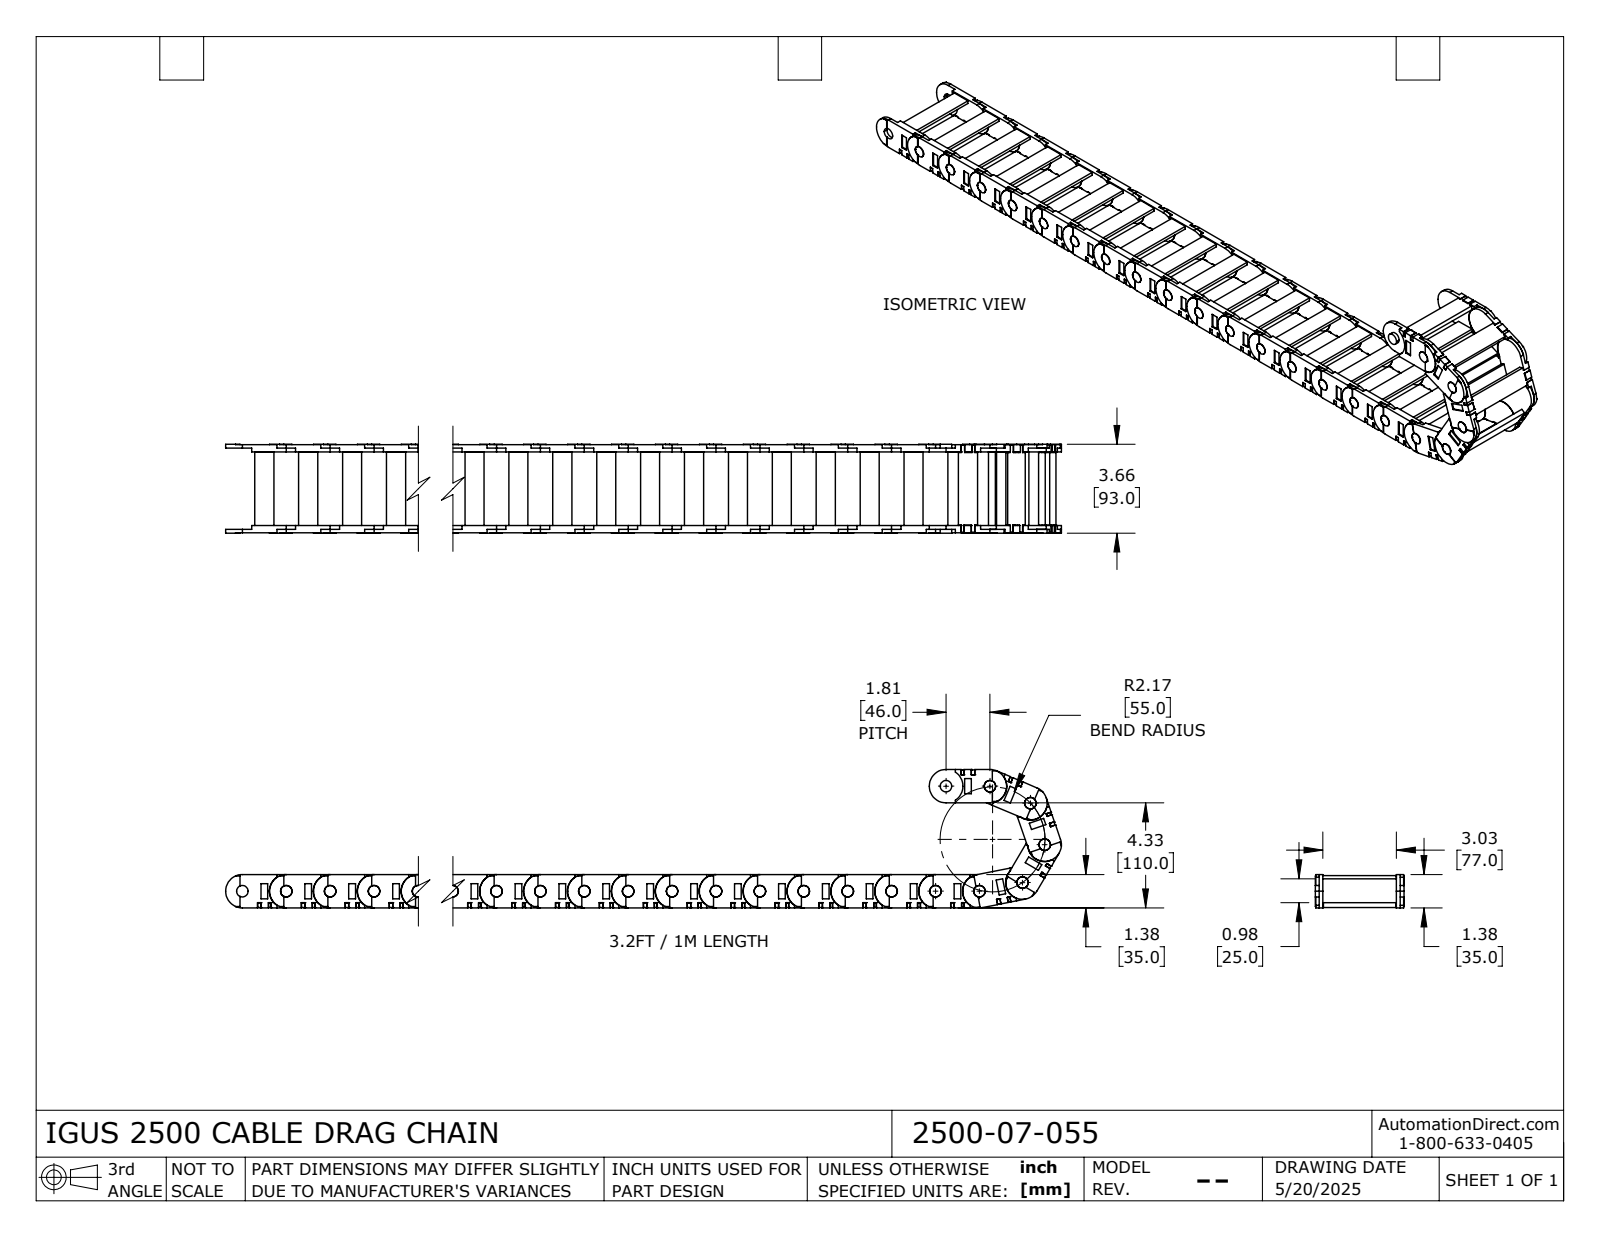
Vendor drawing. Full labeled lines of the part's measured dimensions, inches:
Part name (STEP PRODUCT): 2500_07_055
STEP written by: SolidWorks 2024 (AUTOMOTIVE_DESIGN)
Units: inches
Bodies: 66 solids, 2398 faces (1870 planar, 528 cylindrical, 0 other)
Overall size (bounding box): 34.858 × 5.709 × 3.661
Volume: 49.69 in³ · Surface area: 729.9 in²
Round holes (diameter × count): ⌀0.473 ×22
Round bosses / shafts (diameter × count): ⌀0.472 ×22, ⌀1.378 ×21
Partial cylindrical surfaces — rounded edges, fillets, slot ends (radius × count): R0.697 ×23, R0.689 ×2
Main face-to-face distances: 0.157, 3.189, 3.346, 0.142, 0.299, 3.331, 3.488, 0.197, 0.134, 3.031
Hole centre spacings: 1.811, 3.622, 5.433, 7.244, 9.055, 10.866, 12.677, 14.488
